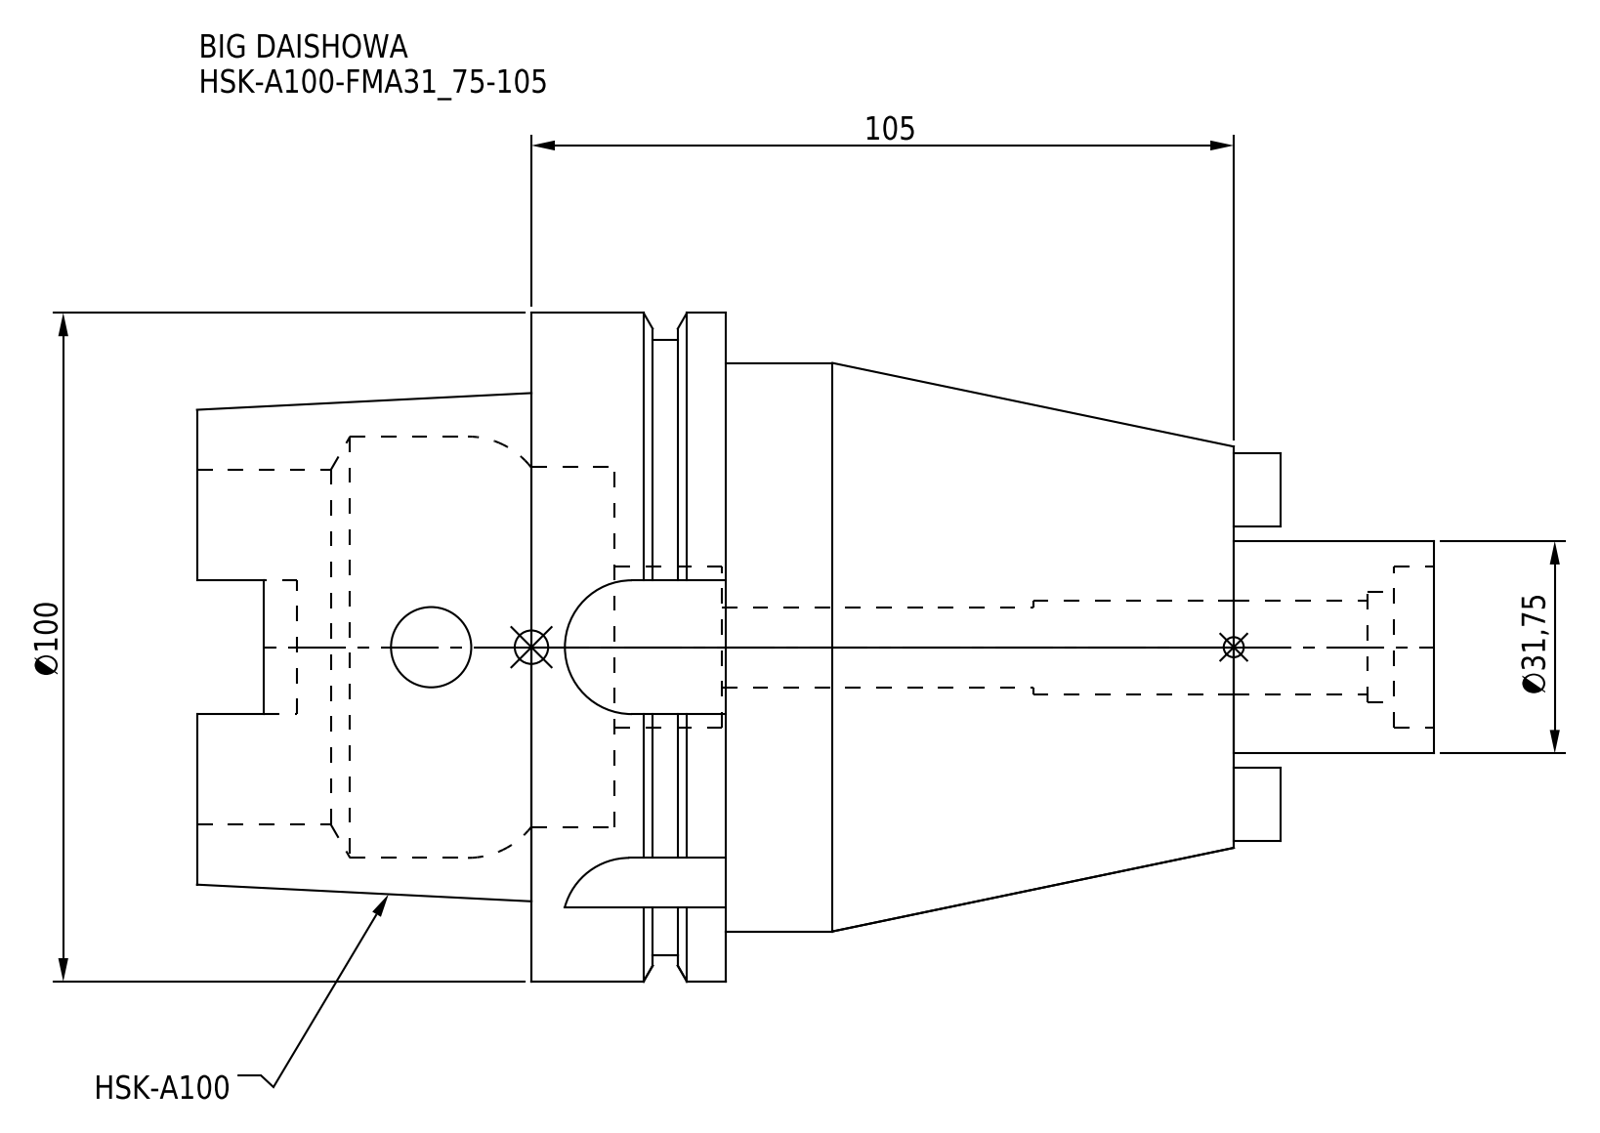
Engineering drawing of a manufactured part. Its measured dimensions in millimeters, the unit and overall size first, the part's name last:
Units: millimetres
Overall size (bounding box): 185 × 100 × 100
Round holes (diameter × count): ⌀12 ×2, ⌀14 ×1, ⌀16.5 ×1, ⌀24 ×1, ⌀53 ×1, ⌀53.8 ×1, ⌀63 ×1
Round bosses / shafts (diameter × count): ⌀100 ×1, ⌀92 ×1, ⌀85 ×1, ⌀31.75 ×1
Partial cylindrical surfaces — rounded edges, fillets, slot ends (radius × count): R4.88 ×4, R10 ×4
Main face-to-face distances: 29, 16.55, 12.45, 76, 92.55, 105, 50, 155, 79, 62.45
Volume: 603 614 mm³ · Surface area: 73 422 mm²
Bodies: 1 solid, 106 faces (46 planar, 44 cylindrical, 16 other)
Part name (STEP PRODUCT): HSK-A100-FMA31_75-105
STEP written by: CREO PARAMETRIC BY PTC INC, 2016380 (AUTOMOTIVE_DESIGN)
